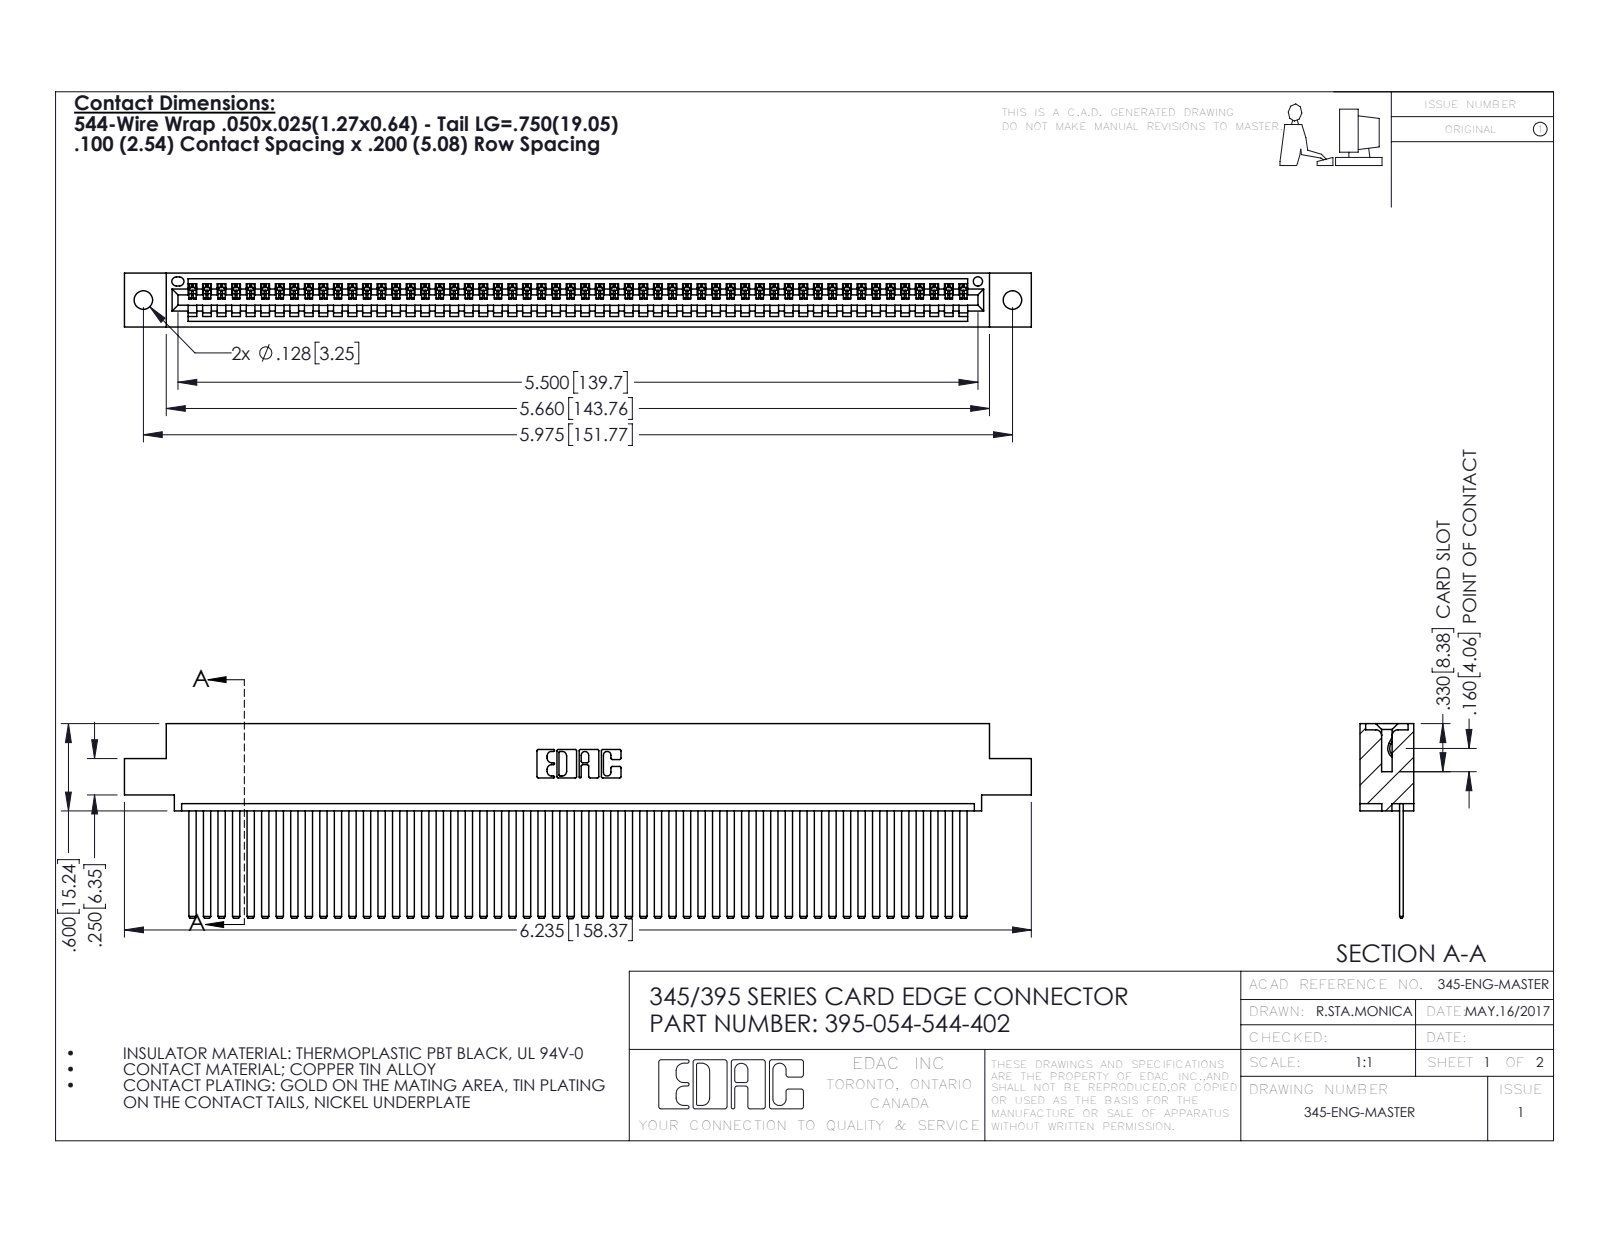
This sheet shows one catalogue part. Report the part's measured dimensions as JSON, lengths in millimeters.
{"part_name": "345 Part_0.110 Offset - 0.128 Dia; 345-292-001_345-293-144; 395-054-544-402", "step_written_by": "SolidWorks 2016 (CONFIG_CONTROL_DESIGN)", "units": "millimeters", "bodies": {"solids": 55, "faces": 2938, "planar": 2028, "cylindrical": 910, "other": 0}, "overall_size": [158.4, 34, 9.4], "volume_mm3": 15600, "surface_area_mm2": 22660, "round_holes": [[3.3, 2], [1.6, 1]], "partial_cylinders_radius": [[0.2, 108], [0.3, 22], [0.2, 6], [0.8, 6], [0.7, 3], [0.8, 2], [1, 2], [0.4, 1]], "face_to_face_distances": [1.8, 7.6, 0.6, 2.5, 6.9, 9.4, 5.1, 5.7, 3.8, 1.8], "hole_center_spacings": [6.9, 145.8, 151.8]}
